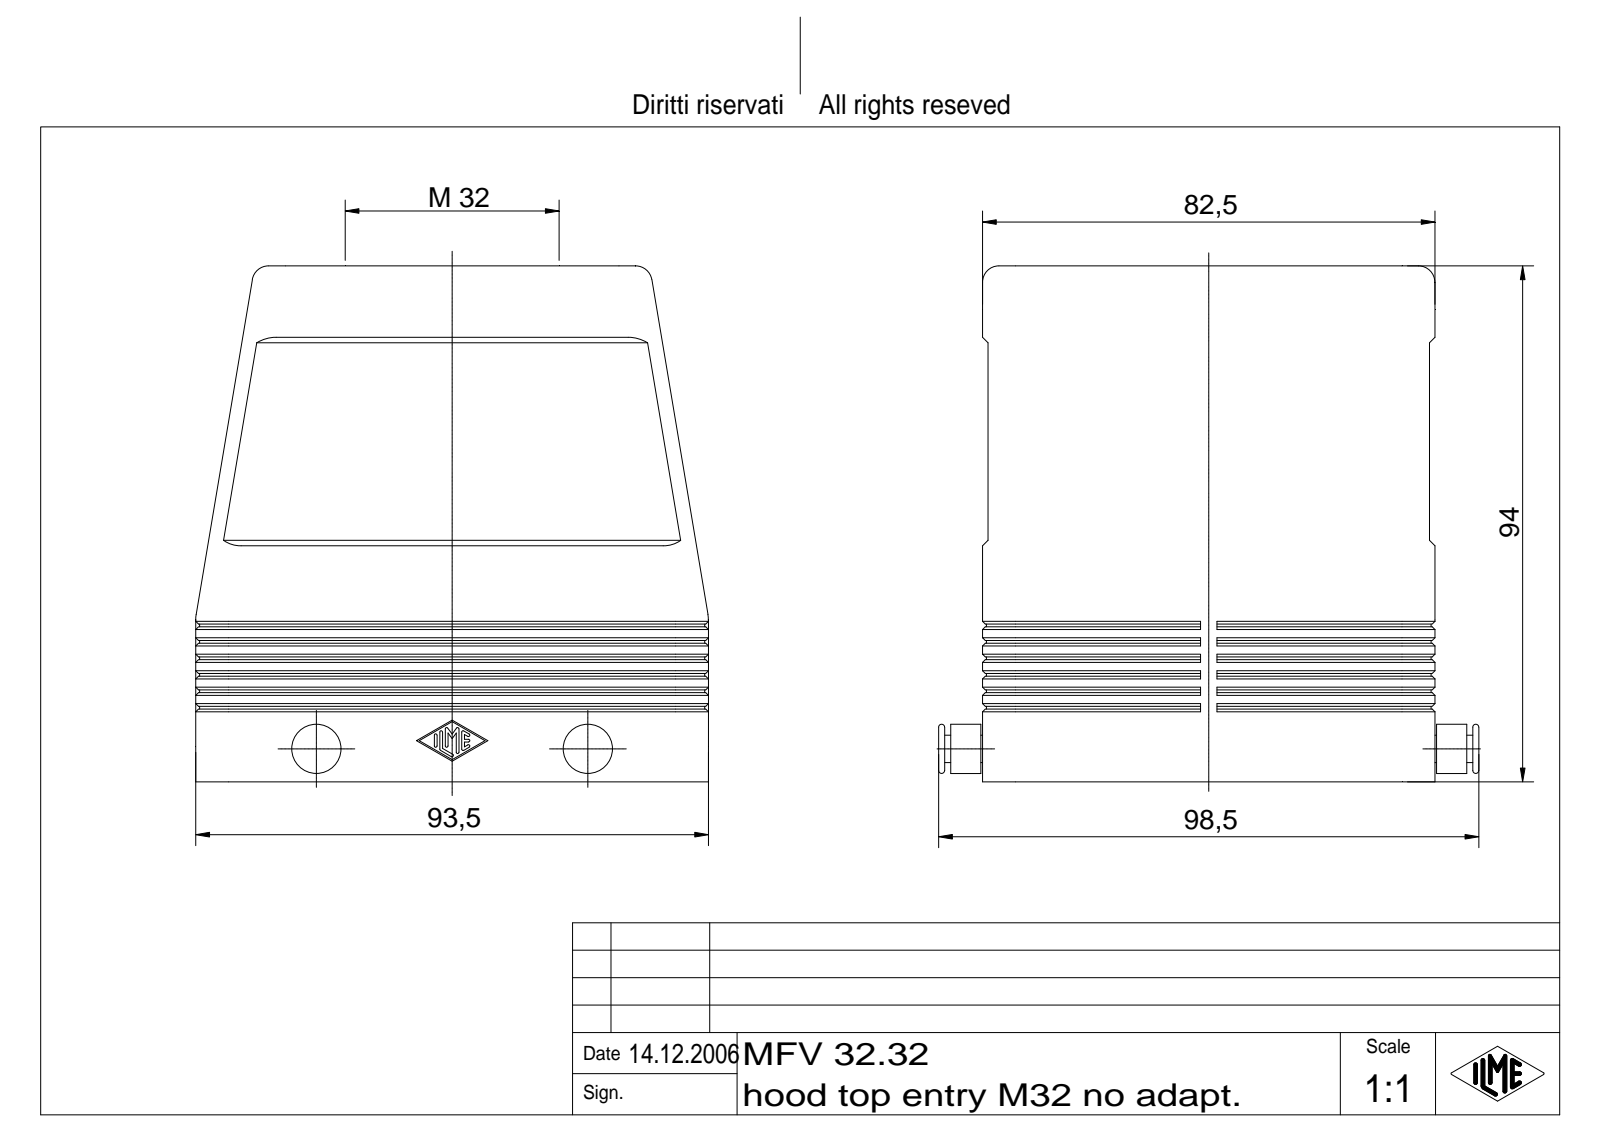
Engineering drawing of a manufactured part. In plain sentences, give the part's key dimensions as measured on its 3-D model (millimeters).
The part is named "MFV 32.32". Its 3-D file was written by "Autodesk Inventor 7 (AUTOMOTIVE_DESIGN)". It is 1 solid with 603 faces: 207 planar, 154 cylindrical and 242 other. Overall it measures 98.5 by 94 by 93.5 millimeters. Its volume is 150 329 cubic millimeters and its surface area 74 904 square millimeters. Round holes: 4 of diameter 2.46, 4 of diameter 3.5, 1 of diameter 39. Round bosses or shafts: 2 of diameter 9, 2 of diameter 5, 1 of diameter 65. Partial cylindrical surfaces (rounded edges, fillets, slot ends): 14 of radius 0.25, 12 of radius 2, 10 of radius 6, 4 of radius 3, 2 of radius 5.3. The main face-to-face distances are 4, 78.5, 74.5, 82.5, 3, 71.5, 11, 1, 77.5, 81.5. The hole center spacings are 27, 38.96, 49.62, 77.5, 82.07.
